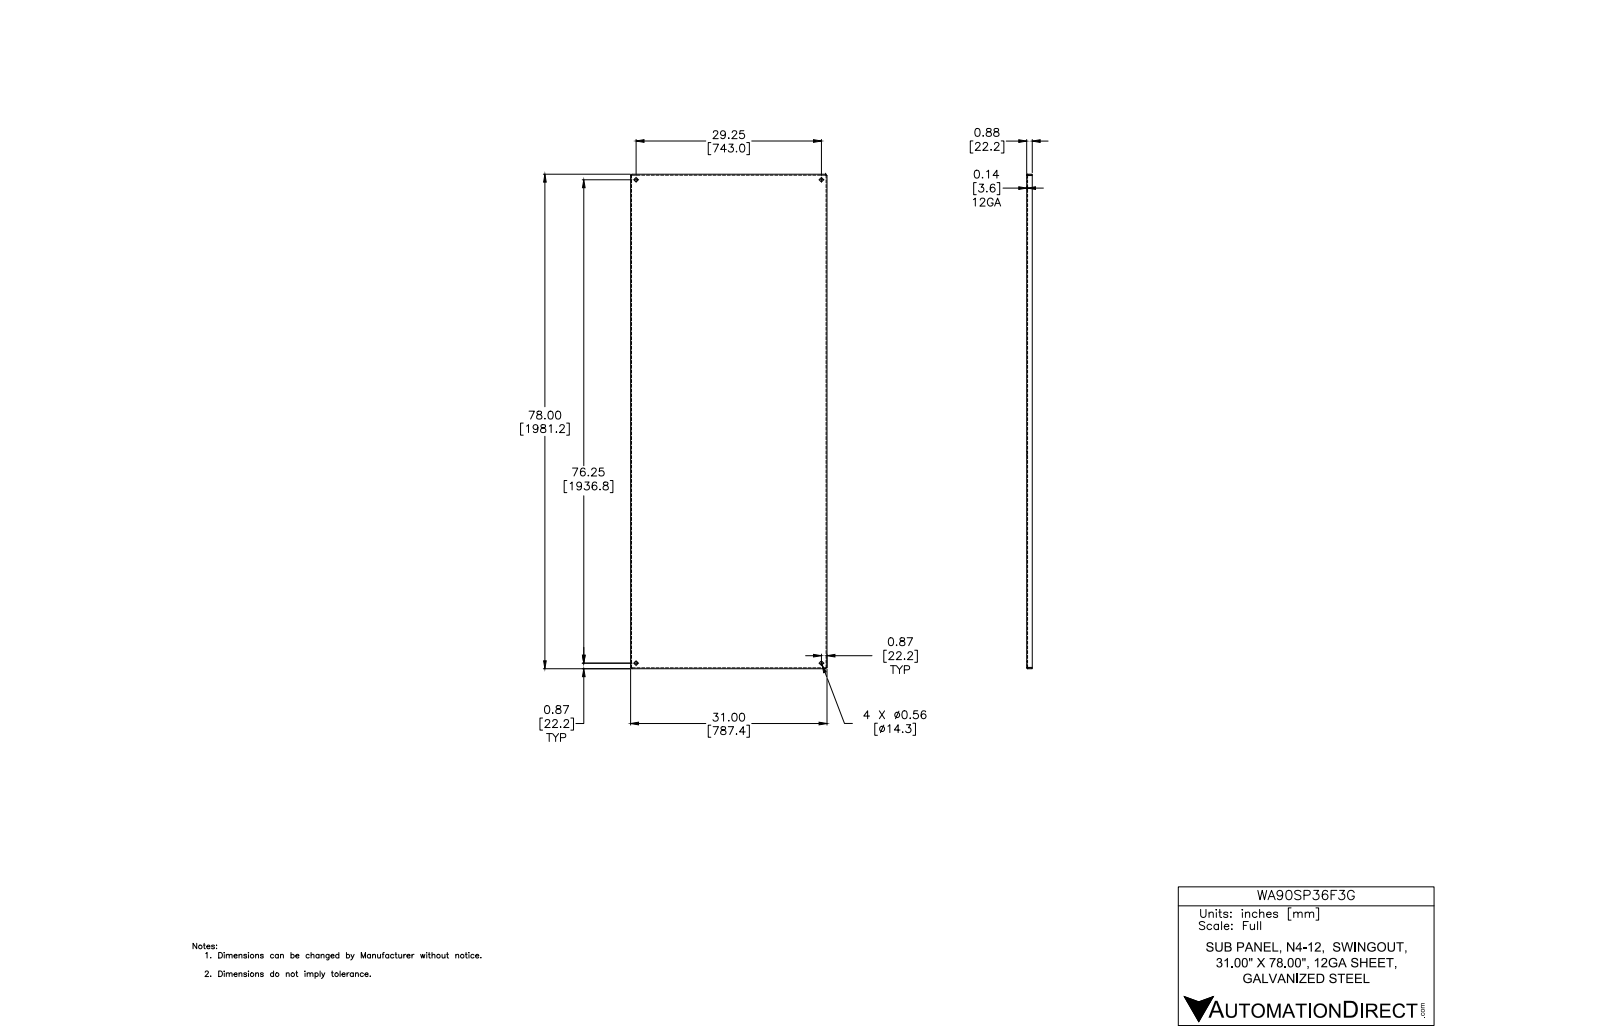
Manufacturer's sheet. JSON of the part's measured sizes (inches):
{"part_name": "WA60SP24F3G-WA90SP36F4G", "step_written_by": "Autodesk Inventor 2012 (AUTOMOTIVE_DESIGN)", "units": "inches", "bodies": {"solids": 1, "faces": 42, "planar": 22, "cylindrical": 12, "other": 8}, "overall_size": [78, 31, 0.875], "volume_in3": 241.8, "surface_area_in2": 5180, "round_holes": [[0.563, 4]], "partial_cylinders_radius": [[0.031, 4], [0.125, 4]], "face_to_face_distances": [0.094, 30.906, 30.813, 31, 77.906, 78, 77.813, 0.781, 0.875, 0.16], "hole_center_spacings": [29.25, 76.25, 81.668]}
